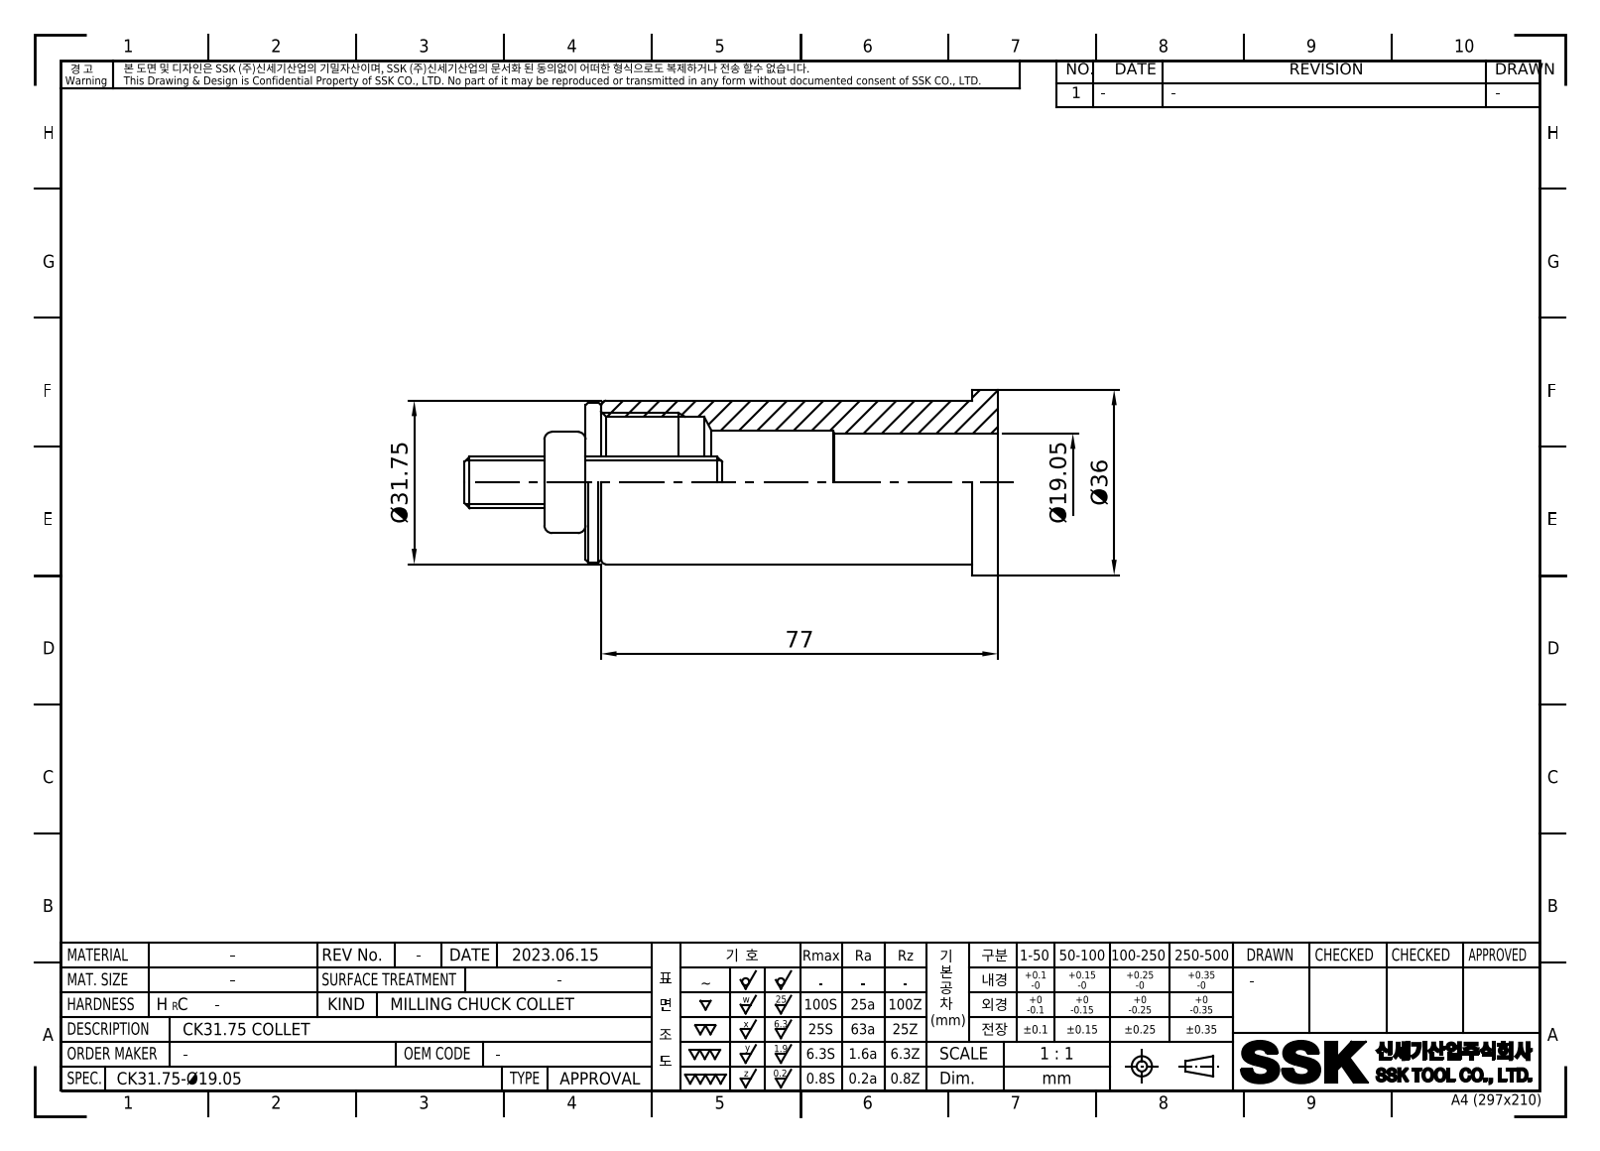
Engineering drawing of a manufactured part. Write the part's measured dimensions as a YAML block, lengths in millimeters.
part_name: "LO-CK31.75-19.05"
step_written_by: "Autodesk Inventor 2022 (AUTOMOTIVE_DESIGN)"
units: millimeters
bodies: {solids: 1, faces: 10, planar: 3, cylindrical: 5, other: 2}
overall_size: [77, 36, 36]
volume: 34851
surface_area: 14211
round_holes:
  - {diameter: 19.05, count: 1}
  - {diameter: 20, count: 1}
  - {diameter: 25.38, count: 1}
round_bosses_or_shafts:
  - {diameter: 36, count: 1}
  - {diameter: 31.75, count: 1}
face_to_face_distances: [77, 72, 5]
